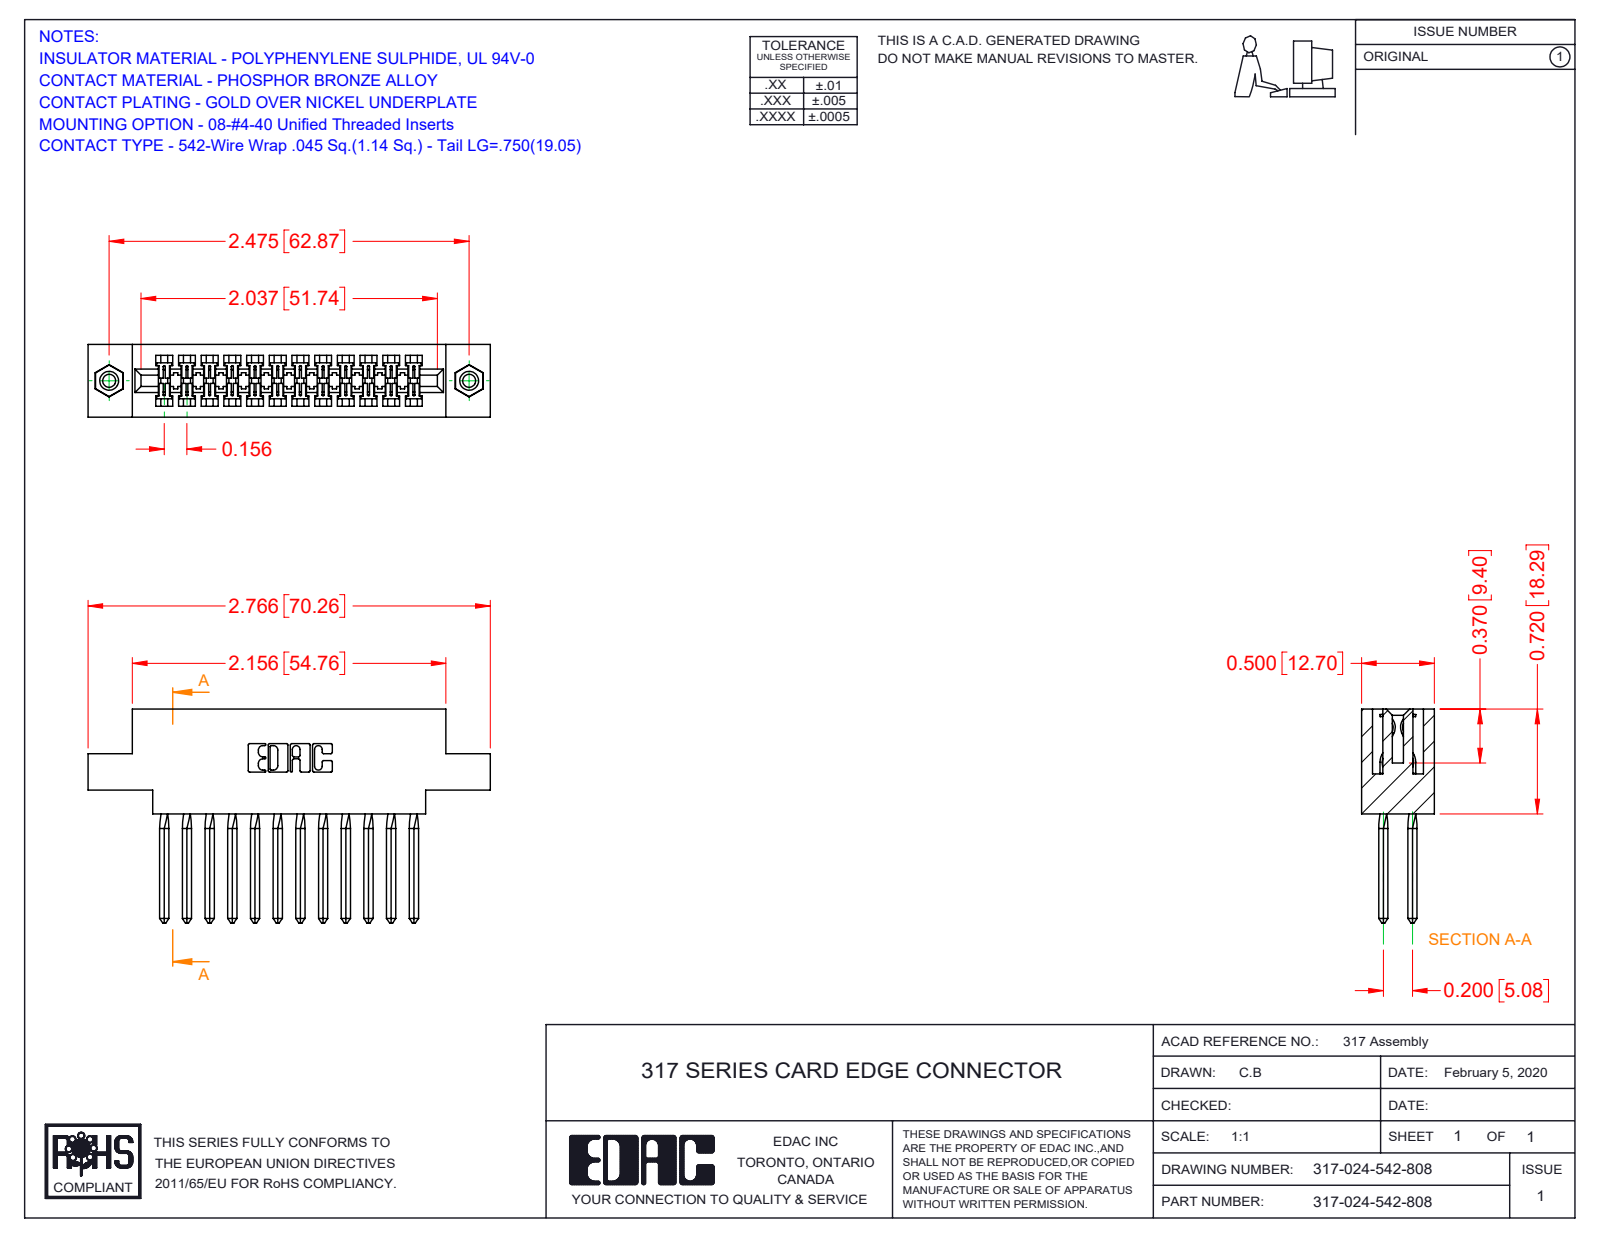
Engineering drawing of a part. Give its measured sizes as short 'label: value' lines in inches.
name: 317-024-542-808; 345-250-001_345-250-003-102; 317 Part_.156 Dia - TI; 317-290-003_542
written by: SolidWorks 2016 (CONFIG_CONTROL_DESIGN)
unit: in
bodies: 27 solids, 1530 faces (1194 planar, 224 cylindrical, 112 other)
size: 2.766 × 1.47 × 0.5
volume: 0.644 in³; area: 21.28 in²
holes: 2× ⌀0.089, 2× ⌀0.125, 2× ⌀0.156
bosses: 2× ⌀0.155
rounds: 48× R0.006, 22× R0.01, 6× R0.007, 6× R0.031, 3× R0.026, 2× R0.074, 2× R0.089, 2× R0.1
face distances: 0.5, 0.075, 0.425, 0.11, 0.35, 0.22, 0.116, 0.2, 0.136, 0.156
hole spacings: 2.475
